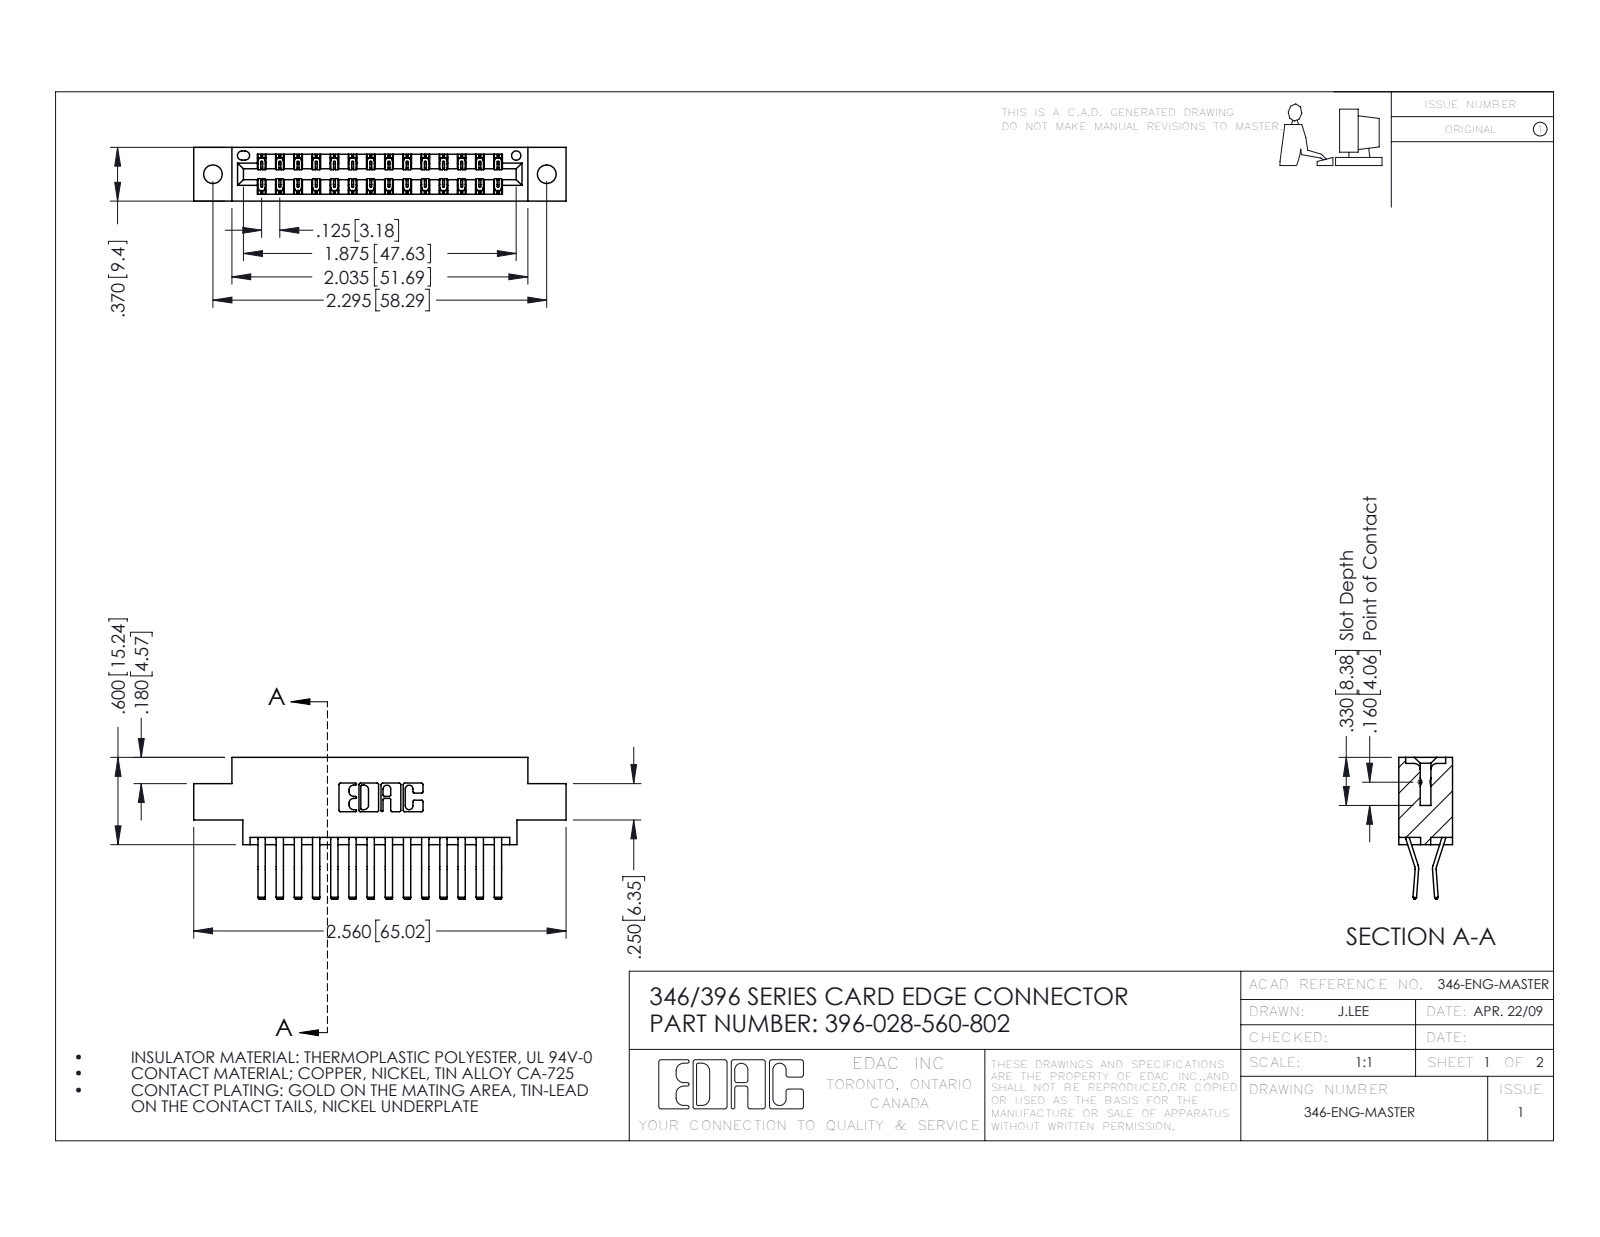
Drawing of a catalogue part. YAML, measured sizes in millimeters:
part_name: "396-028-560-802; 346 Part_0.170 Offset - 0.128 Dia; 345-292-001_560 Tail"
step_written_by: "SolidWorks 2016 (CONFIG_CONTROL_DESIGN)"
units: millimeters
bodies: {solids: 29, faces: 1638, planar: 1060, cylindrical: 578, other: 0}
overall_size: [65, 24.8, 9.4]
volume: 6110
surface_area: 8368
round_holes:
  - {diameter: 3.3, count: 2}
  - {diameter: 1.6, count: 1}
partial_cylinders:
  - {radius: 0.2, count: 42}
  - {radius: 0.3, count: 22}
  - {radius: 0.2, count: 6}
  - {radius: 0.8, count: 6}
  - {radius: 0.7, count: 3}
  - {radius: 0.3, count: 2}
  - {radius: 0.4, count: 2}
  - {radius: 0.6, count: 2}
face_to_face_distances: [1.2, 8.2, 9.4, 6.4, 0.6, 1.8, 7.6, 7, 3.8, 5.6]
hole_center_spacings: [6.2, 53.1, 58.3]
